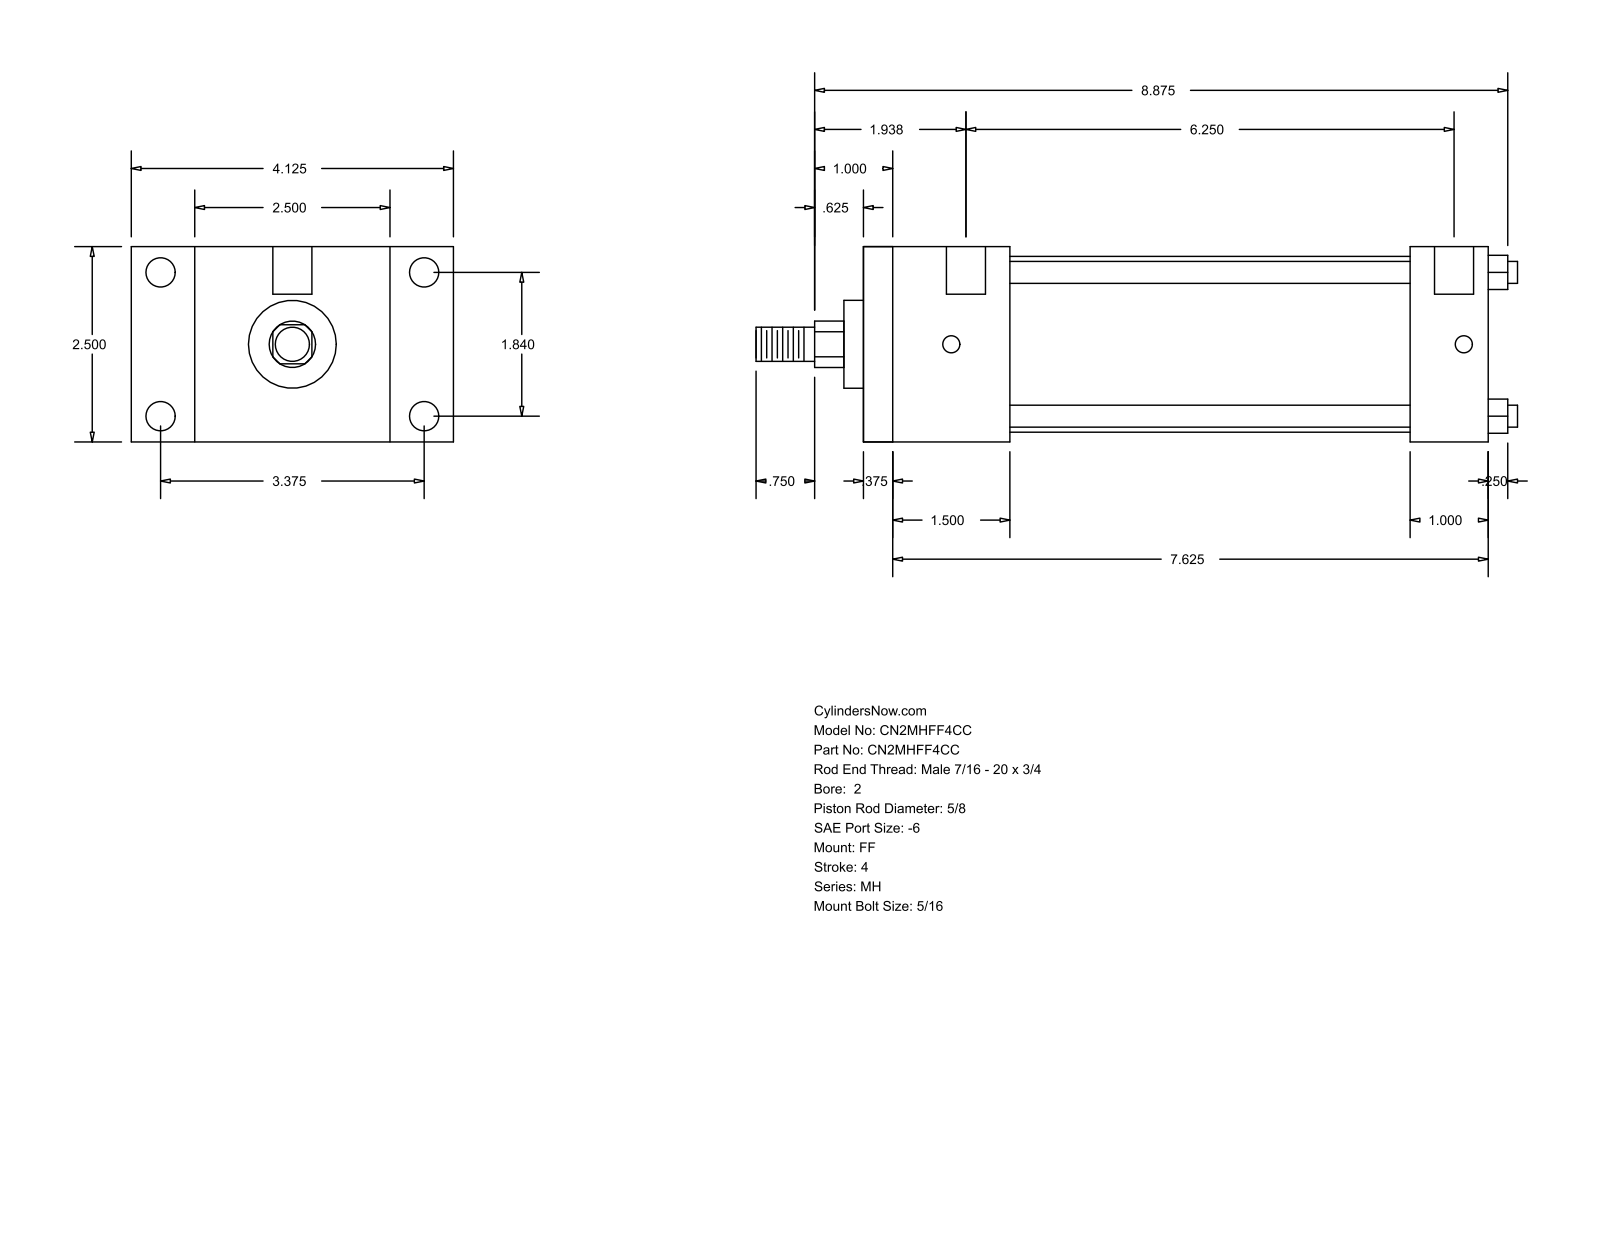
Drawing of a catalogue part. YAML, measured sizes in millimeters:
part_name: "MH_FF__0200_0.625"
step_written_by: "GSSL Pune (CONFIG_CONTROL_DESIGN)"
units: millimeters
bodies: {solids: 0, faces: 92, planar: 64, cylindrical: 28, other: 0}
overall_size: [247.65, 104.78, 63.5]
round_holes:
  - {diameter: 5.56, count: 4}
  - {diameter: 9.53, count: 4}
  - {diameter: 12.7, count: 2}
round_bosses_or_shafts:
  - {diameter: 7.14, count: 4}
  - {diameter: 57.15, count: 1}
  - {diameter: 28.57, count: 1}
  - {diameter: 15.88, count: 1}
  - {diameter: 11.11, count: 1}
partial_cylinders:
  - {radius: 7.54, count: 1}
face_to_face_distances: [63.5, 203.19, 9.52, 193.67, 38.1, 47.62, 177.8, 168.28, 130.18, 155.57]
hole_center_spacings: [46.74, 85.72, 97.63, 166.69, 3.18, 4.76, 158.75, 161.93]
